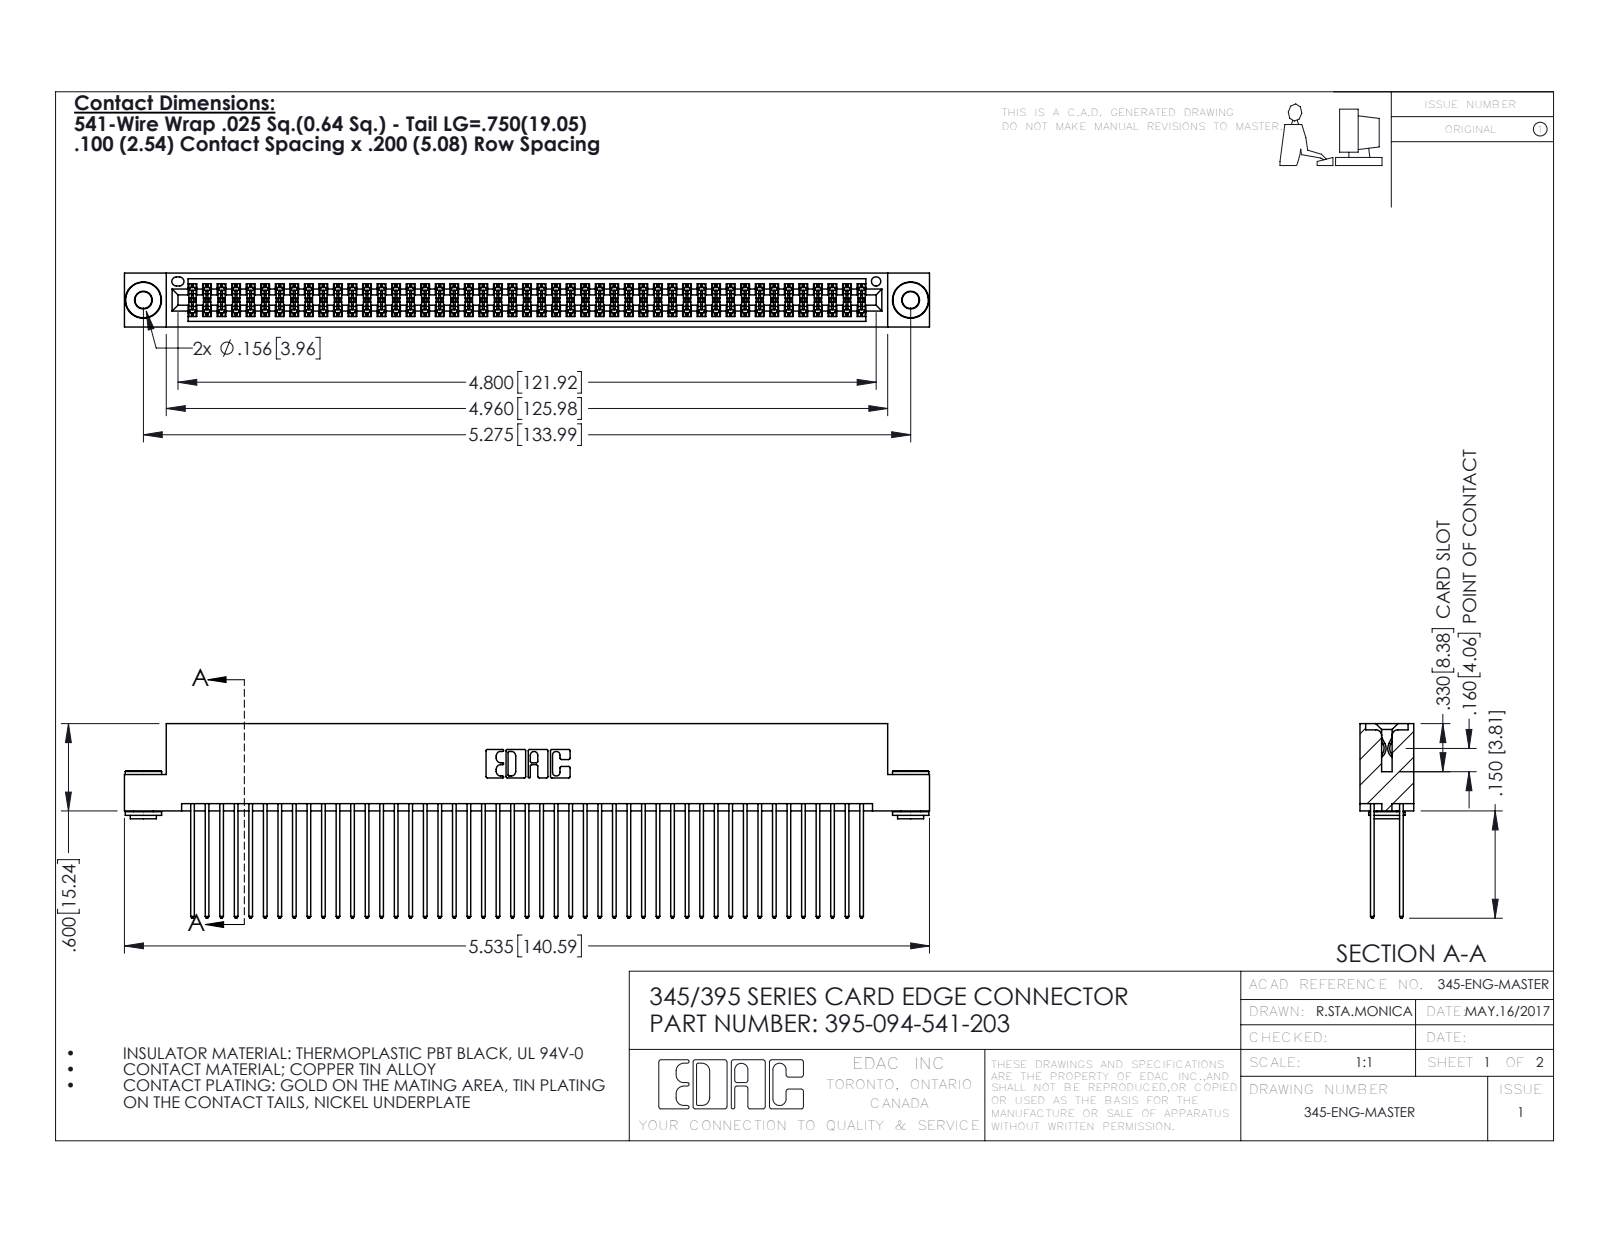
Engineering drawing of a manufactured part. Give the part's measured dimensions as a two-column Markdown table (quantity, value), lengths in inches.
| quantity | value |
| --- | --- |
| part name | 345 Part_Flush Mounting Lugs - 0.156 Dia-TH; 345-292-001_345-293-141; 345-250-002_345-250-002-102; 395-094-541-203 |
| STEP written by | SolidWorks 2016 (CONFIG_CONTROL_DESIGN) |
| units | inches |
| bodies | 97 solids, 4864 faces (3192 planar, 1664 cylindrical, 8 other) |
| overall size | 5.535 × 1.337 × 0.37 |
| volume | 0.87 in³ |
| surface area | 37.07 in² |
| round holes (diameter × count) | 0.116 × 2, 0.156 × 2, 0.064 × 1 |
| round bosses / shafts (diameter × count) | 0.25 × 2, 0.18 × 2, 0.136 × 2 |
| partial cylindrical surfaces (radius × count) | 0.006 × 141, 0.01 × 94, 0.01 × 22, 0.007 × 6, 0.031 × 6, 0.026 × 3, 0.014 × 2, 0.019 × 2 |
| main face-to-face distances | 0.072, 0.298, 0.2, 0.025, 0.098, 0.272, 0.225, 0.37, 0.175, 0.149 |
| hole center spacings | 0.27, 5.039, 5.275 |
